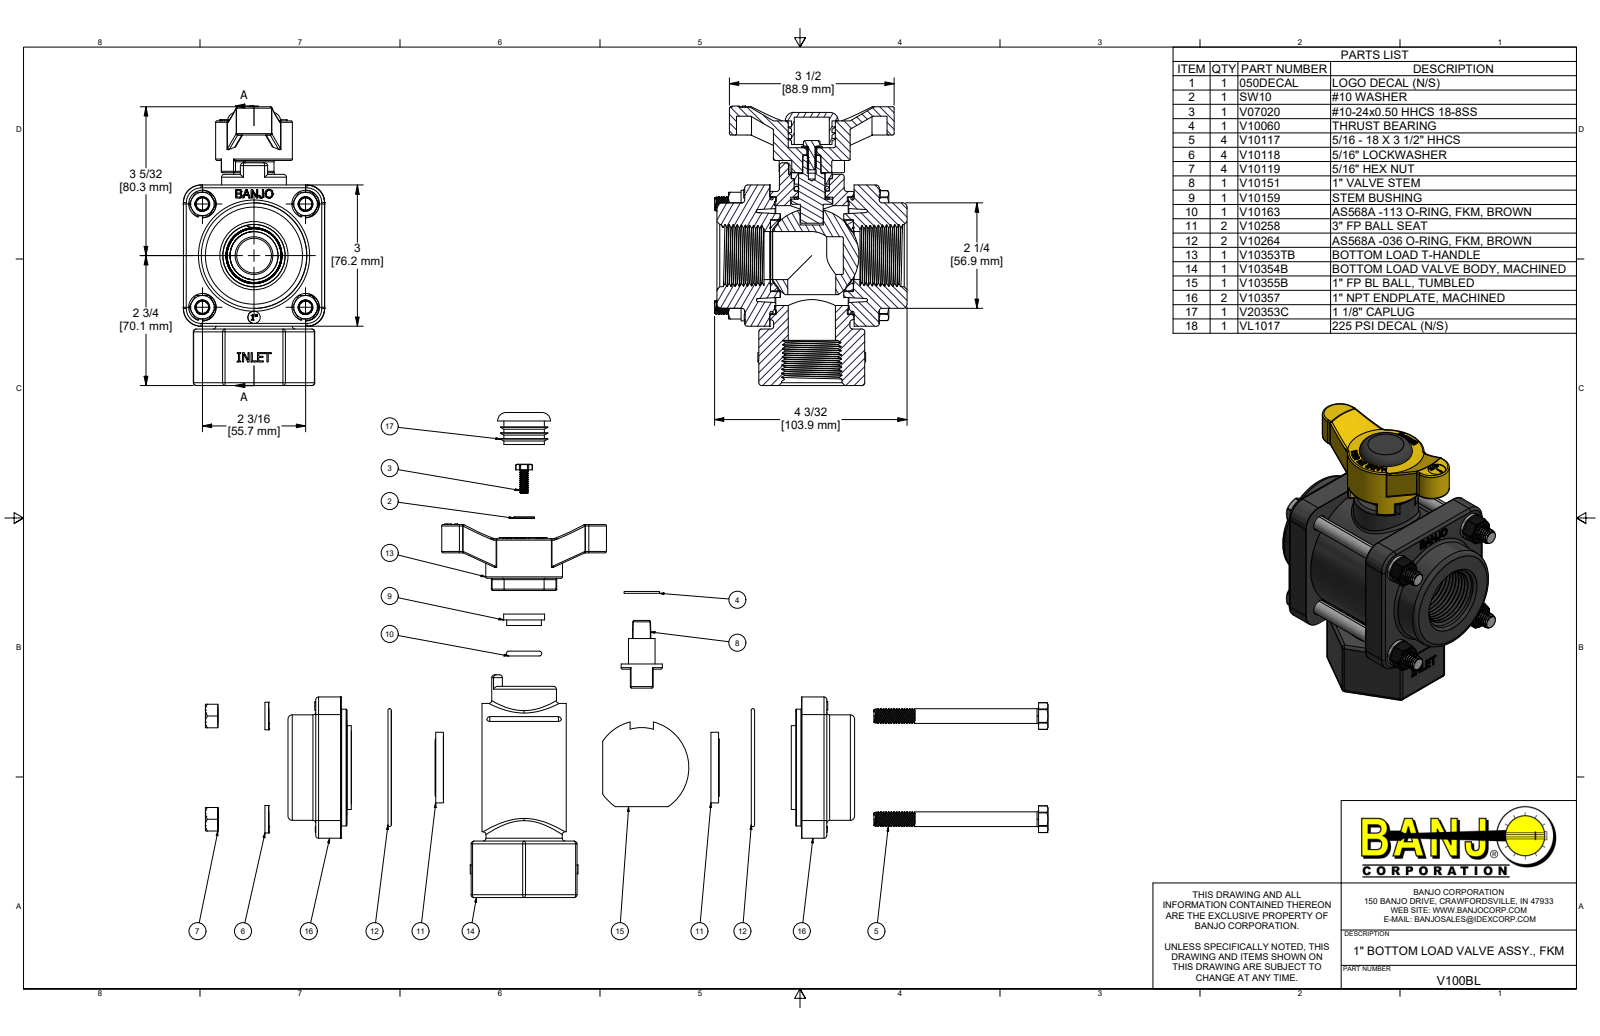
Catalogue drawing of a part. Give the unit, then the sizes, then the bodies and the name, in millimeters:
Units: millimetres
Overall size (bounding box): 150.8 × 103.9 × 76.2
Round holes (diameter × count): ⌀6.4 ×4, ⌀8.2 ×4, ⌀9.3 ×4, ⌀25.9 ×2, ⌀2.3 ×1, ⌀3.3 ×1, ⌀3.7 ×1, ⌀5.2 ×1, ⌀5.3 ×1, ⌀6.6 ×1, ⌀9.5 ×1, ⌀14.3 ×1
Round bosses / shafts (diameter × count): ⌀6.8 ×60, ⌀14.8 ×4, ⌀8 ×4, ⌀69.2 ×1, ⌀63 ×1, ⌀58.5 ×1, ⌀56.9 ×1, ⌀45.2 ×1
Partial cylindrical surfaces — rounded edges, fillets, slot ends (radius × count): R0.8 ×66, R1.5 ×52, R0.8 ×12, R3.4 ×8, R9.5 ×6, R7.2 ×4, R0.4 ×3, R0.3 ×2
Main face-to-face distances: 13.6, 60.3, 3.2, 16.8, 57.1, 43.5, 76.2, 57.2, 73.9, 46.7
Hole centre spacings: 39.4, 55.7, 28.4, 67.2, 78.7, 16.8, 33.3, 38.9
Volume: 436 600 mm³ · Surface area: 145 000 mm²
Bodies: 28 solids, 2434 faces (924 planar, 647 cylindrical, 863 other)
Part name (STEP PRODUCT): V100BL; V10354B; V10354BX; V10357 (+8 more)
STEP written by: Autodesk Inventor 2022 (AUTOMOTIVE_DESIGN)
